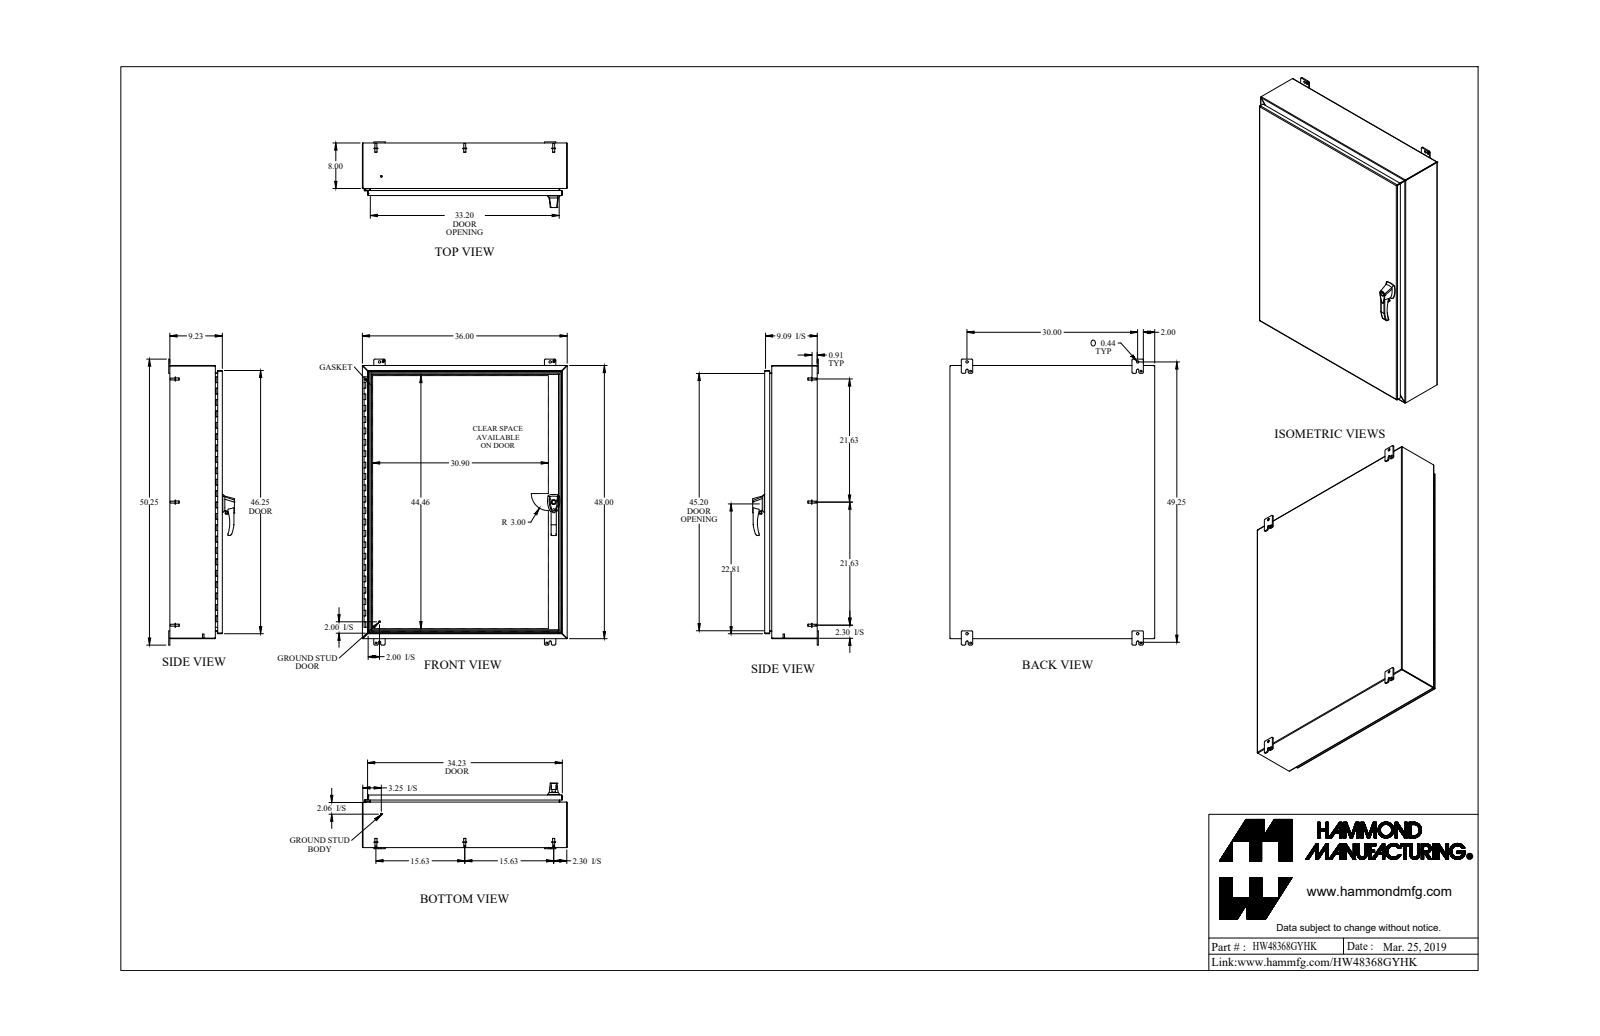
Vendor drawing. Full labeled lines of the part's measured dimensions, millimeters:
Part name (STEP PRODUCT): HW48368GYHK
STEP written by: SolidWorks 2018 (AUTOMOTIVE_DESIGN)
Units: millimetres
Bodies: 48 solids, 1768 faces (837 planar, 734 cylindrical, 197 other)
Overall size (bounding box): 1276.4 × 914.4 × 293
Volume: 7 907 000 mm³ · Surface area: 7 643 000 mm²
Round holes (diameter × count): ⌀4.5 ×6, ⌀6.4 ×4, ⌀8 ×4, ⌀5 ×3, ⌀6.7 ×3, ⌀10.5 ×3, ⌀6.5 ×2, ⌀10 ×2, ⌀11.1 ×2, ⌀4.7 ×1, ⌀5.9 ×1, ⌀8.5 ×1
Round bosses / shafts (diameter × count): ⌀9.5 ×13, ⌀16.5 ×8, ⌀8.4 ×8, ⌀6.4 ×6, ⌀4 ×6, ⌀25.4 ×3, ⌀16 ×2, ⌀13 ×2
Partial cylindrical surfaces — rounded edges, fillets, slot ends (radius × count): R6.4 ×31, R4.8 ×26, R0.9 ×16, R2.7 ×16, R1.5 ×12, R2.9 ×12, R4.7 ×10, R3.2 ×9
Main face-to-face distances: 1.8, 232.1, 230.3, 2.4, 234.5, 232.7, 912.6, 1217.4, 201.4, 910.7
Hole centre spacings: 511, 511, 1022, 28.2, 218.1, 511, 762, 778.8
